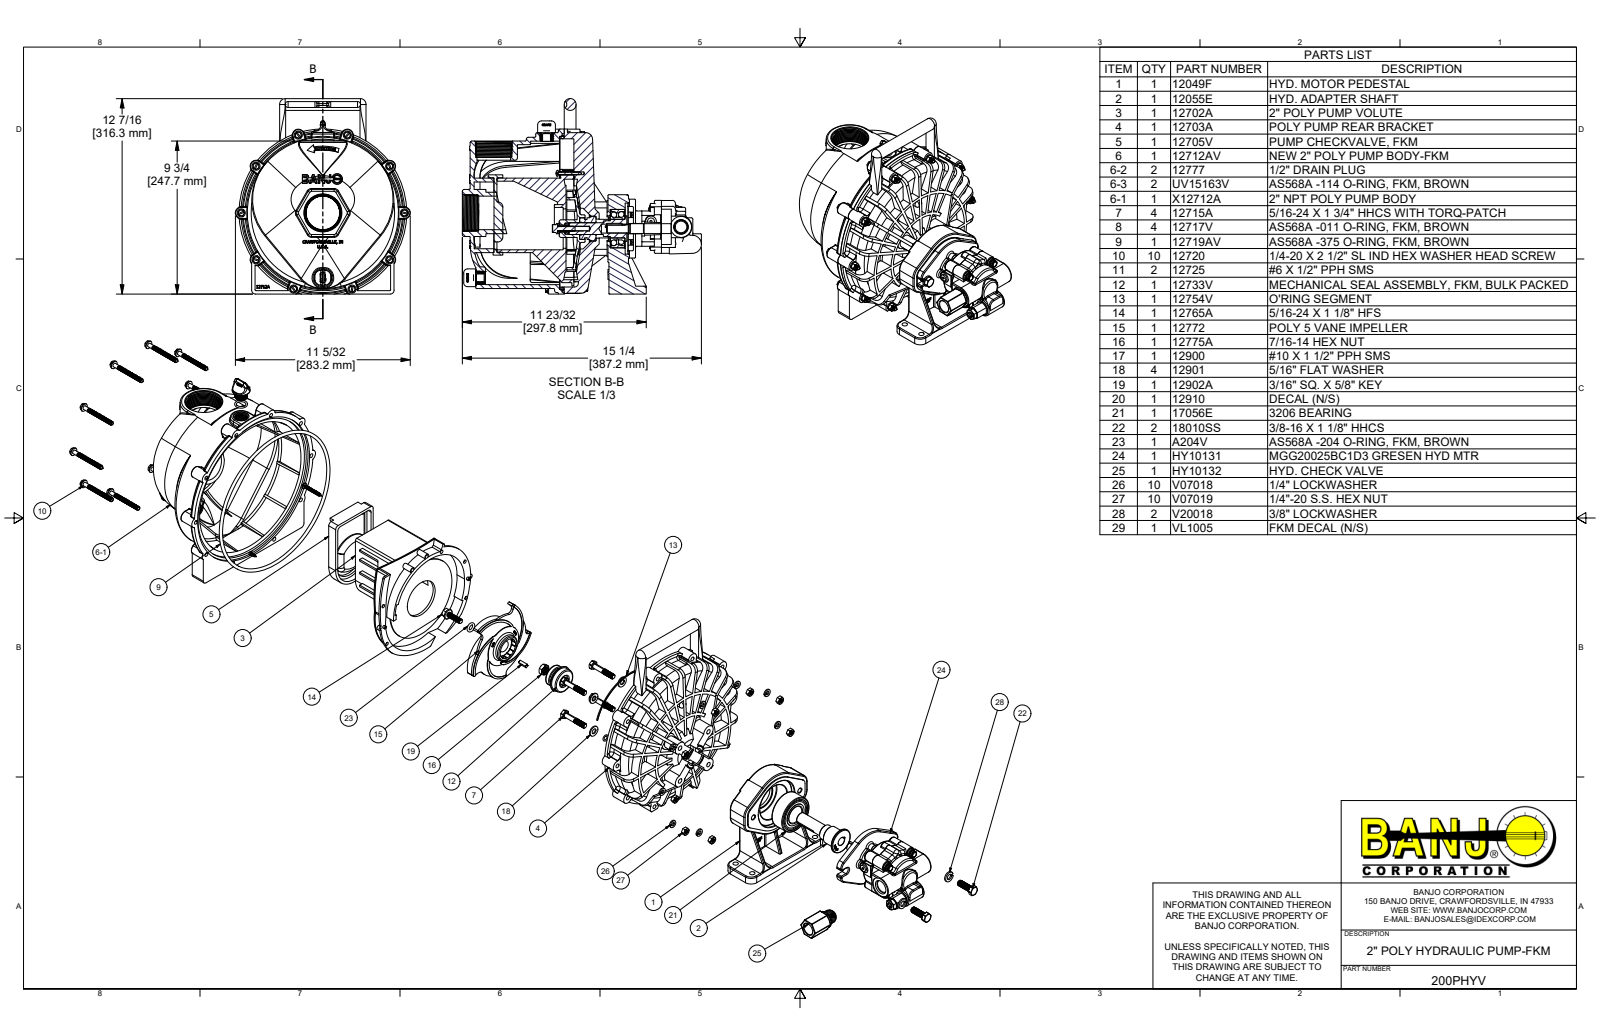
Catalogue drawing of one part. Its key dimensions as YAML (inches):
part_name: "200PHYV; 12703A; 12712AV; X12712A (+8 more)"
step_written_by: "Autodesk Inventor 2022 (AUTOMOTIVE_DESIGN)"
units: inches
bodies: {solids: 113, faces: 9661, planar: 2727, cylindrical: 2711, other: 4223}
overall_size: [15.243, 12.452, 11.15]
volume: 235.4
surface_area: 2005
round_holes:
  - {diameter: 0.196, count: 10}
  - {diameter: 0.252, count: 10}
  - {diameter: 0.27, count: 10}
  - {diameter: 0.344, count: 8}
  - {diameter: 0.235, count: 7}
  - {diameter: 0.267, count: 5}
  - {diameter: 0.469, count: 4}
  - {diameter: 0.815, count: 4}
  - {diameter: 0.113, count: 2}
  - {diameter: 0.115, count: 2}
  - {diameter: 0.205, count: 2}
  - {diameter: 0.25, count: 2}
round_bosses_or_shafts:
  - {diameter: 0.276, count: 80}
  - {diameter: 0.324, count: 34}
  - {diameter: 0.52, count: 10}
  - {diameter: 0.489, count: 10}
  - {diameter: 0.25, count: 10}
  - {diameter: 0.312, count: 8}
  - {diameter: 0.192, count: 6}
  - {diameter: 0.688, count: 4}
partial_cylinders:
  - {radius: 0.03, count: 179}
  - {radius: 0.062, count: 105}
  - {radius: 0.25, count: 39}
  - {radius: 0.06, count: 37}
  - {radius: 0.125, count: 27}
  - {radius: 0.008, count: 26}
  - {radius: 0.187, count: 24}
  - {radius: 0.062, count: 17}
face_to_face_distances: [0.2, 0.5, 1, 0.125, 0.18, 0.25, 0.11, 0.61, 0.037, 0.163]
hole_center_spacings: [5.2, 3.127, 6.15, 10.4, 1.5, 1.81, 1.81, 2.559]
